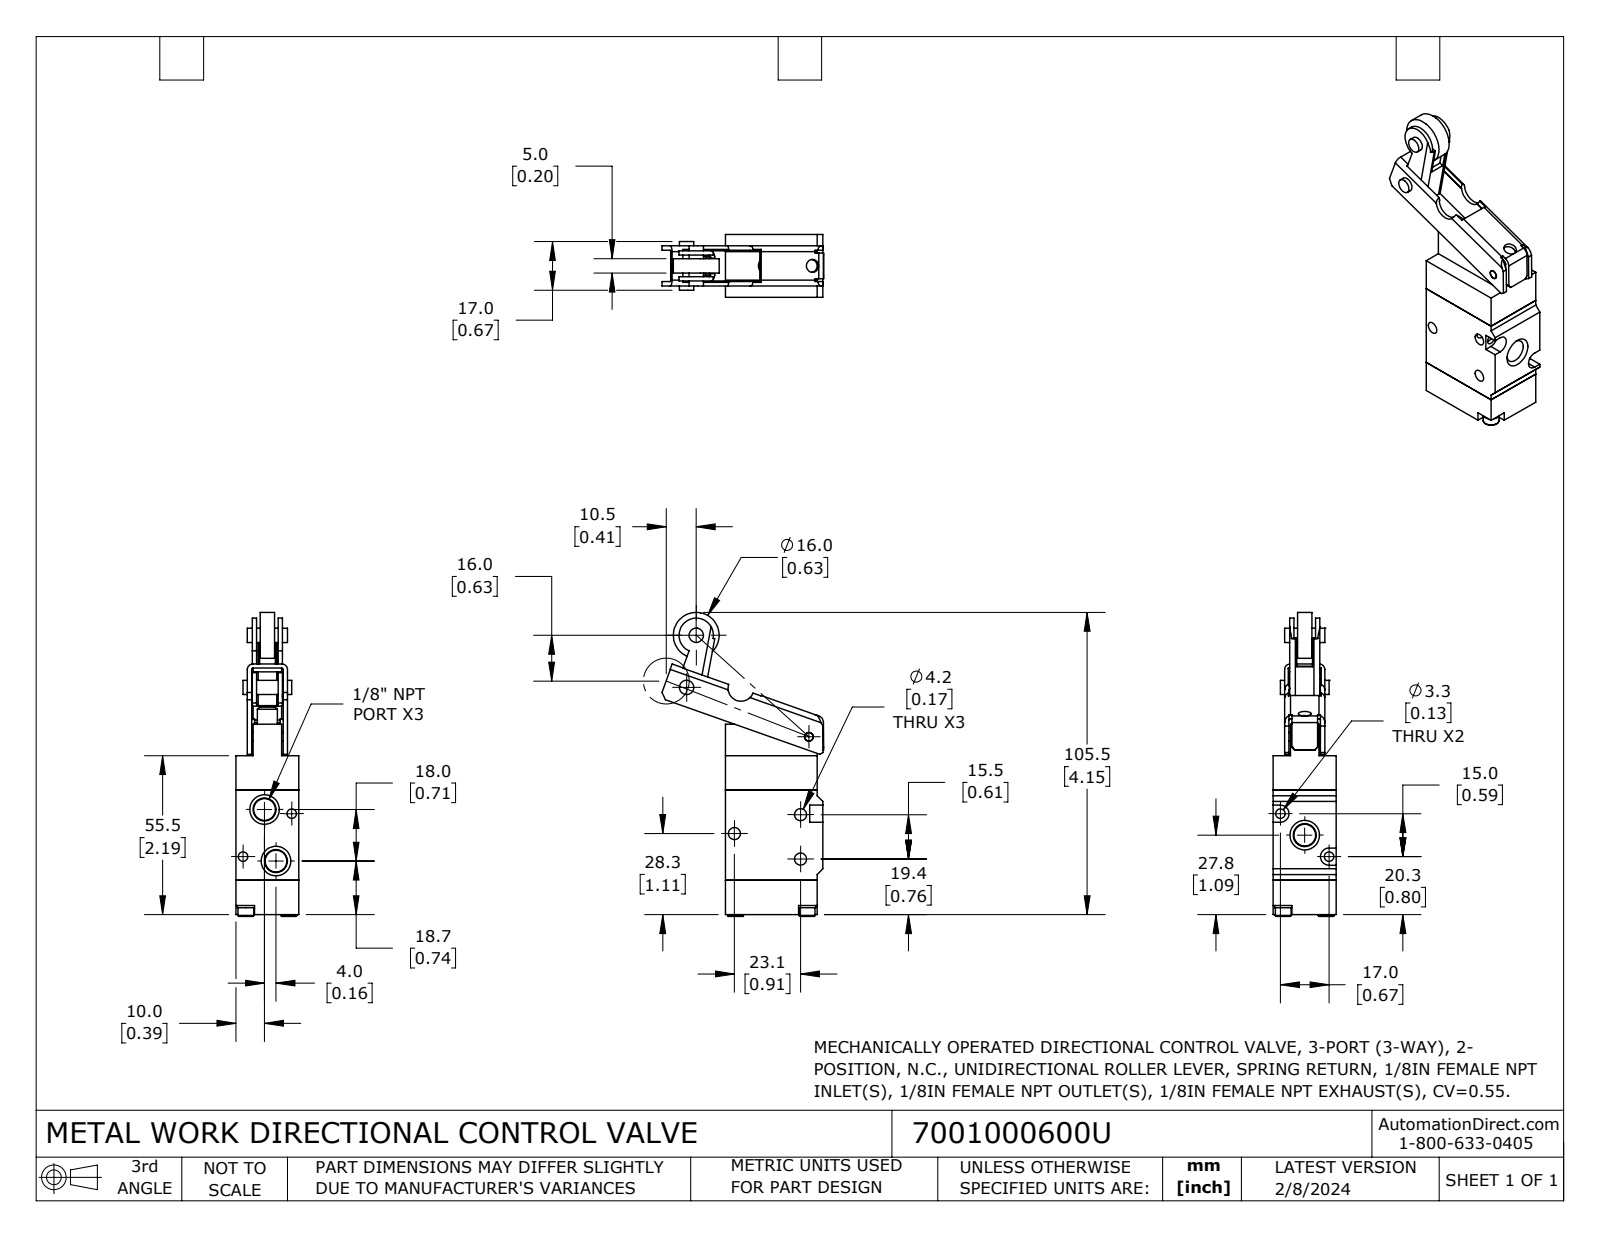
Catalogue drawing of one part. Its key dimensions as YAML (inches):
part_name: "7001000600U"
step_written_by: "SolidWorks 2023 (CONFIG_CONTROL_DESIGN)"
units: inches
bodies: {solids: 9, faces: 260, planar: 132, cylindrical: 86, other: 42}
overall_size: [4.177, 2.223, 0.866]
volume: 2.816
surface_area: 31.28
round_holes:
  - {diameter: 0.118, count: 3}
  - {diameter: 0.165, count: 3}
  - {diameter: 0.13, count: 2}
  - {diameter: 0.177, count: 1}
round_bosses_or_shafts:
  - {diameter: 0.236, count: 2}
  - {diameter: 0.217, count: 2}
  - {diameter: 0.197, count: 2}
  - {diameter: 0.63, count: 1}
  - {diameter: 0.276, count: 1}
partial_cylinders:
  - {radius: 0.02, count: 4}
  - {radius: 0.079, count: 4}
  - {radius: 0.118, count: 2}
  - {radius: 0.039, count: 1}
  - {radius: 0.098, count: 1}
  - {radius: 0.177, count: 1}
  - {radius: 0.217, count: 1}
  - {radius: 0.236, count: 1}
face_to_face_distances: [0.059, 0.866, 0.472, 1.24, 0.157, 0.709, 0.217, 0.65, 0.492, 0.079]
hole_center_spacings: [0.61, 0.893, 0.946, 0.975, 1.076, 1.148, 1.678, 1.684]
